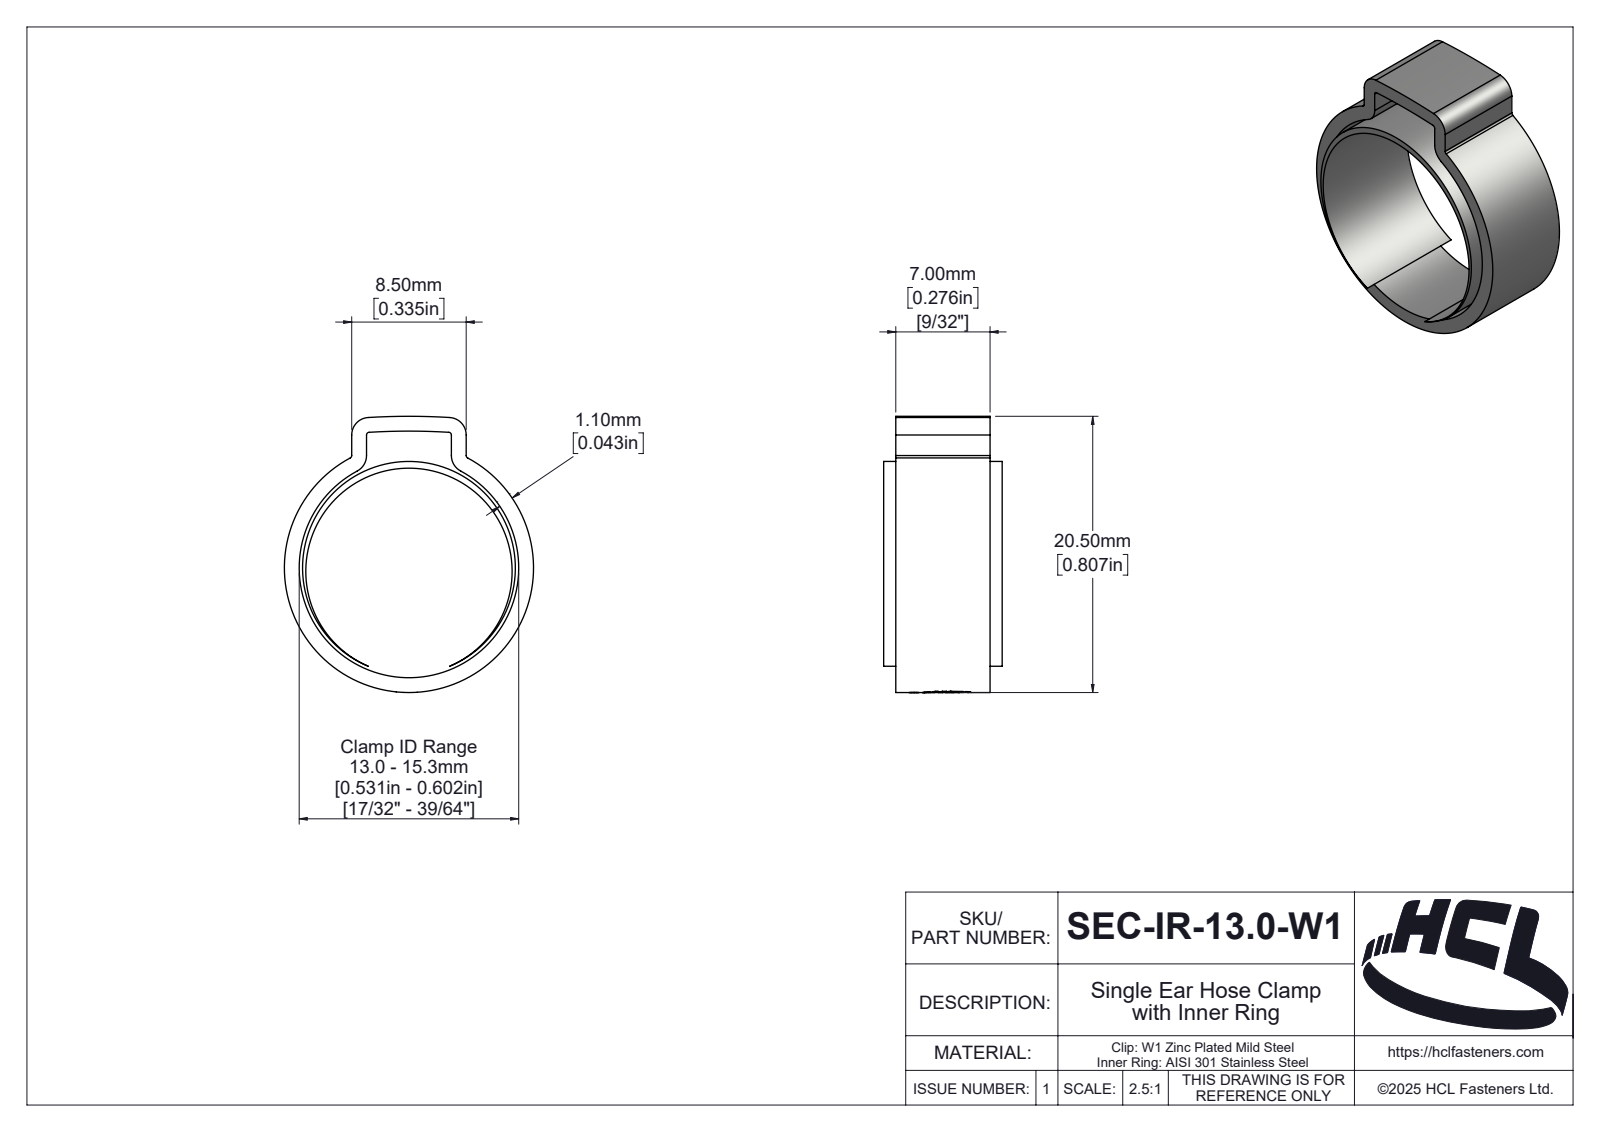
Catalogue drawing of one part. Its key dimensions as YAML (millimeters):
part_name: "SEC-IR-13.5-W1"
step_written_by: "SolidWorks 2025 (AUTOMOTIVE_DESIGN)"
units: millimeters
bodies: {solids: 2, faces: 131, planar: 10, cylindrical: 72, other: 49}
overall_size: [20.5, 18.5, 8.8]
volume: 558
surface_area: 1735
round_holes:
  - {diameter: 15.32, count: 1}
  - {diameter: 16.3, count: 1}
round_bosses_or_shafts:
  - {diameter: 18.5, count: 1}
  - {diameter: 15.8, count: 1}
partial_cylinders:
  - {radius: 0.2, count: 4}
  - {radius: 1.3, count: 4}
  - {radius: 0.2, count: 1}
  - {radius: 0.81, count: 1}
  - {radius: 1.01, count: 1}
  - {radius: 1.06, count: 1}
  - {radius: 1.28, count: 1}
  - {radius: 1.81, count: 1}
face_to_face_distances: [7, 0.9, 7.9, 1.1, 7.4, 8.8, 8.5, 6.3, 3.98, 2.88]
